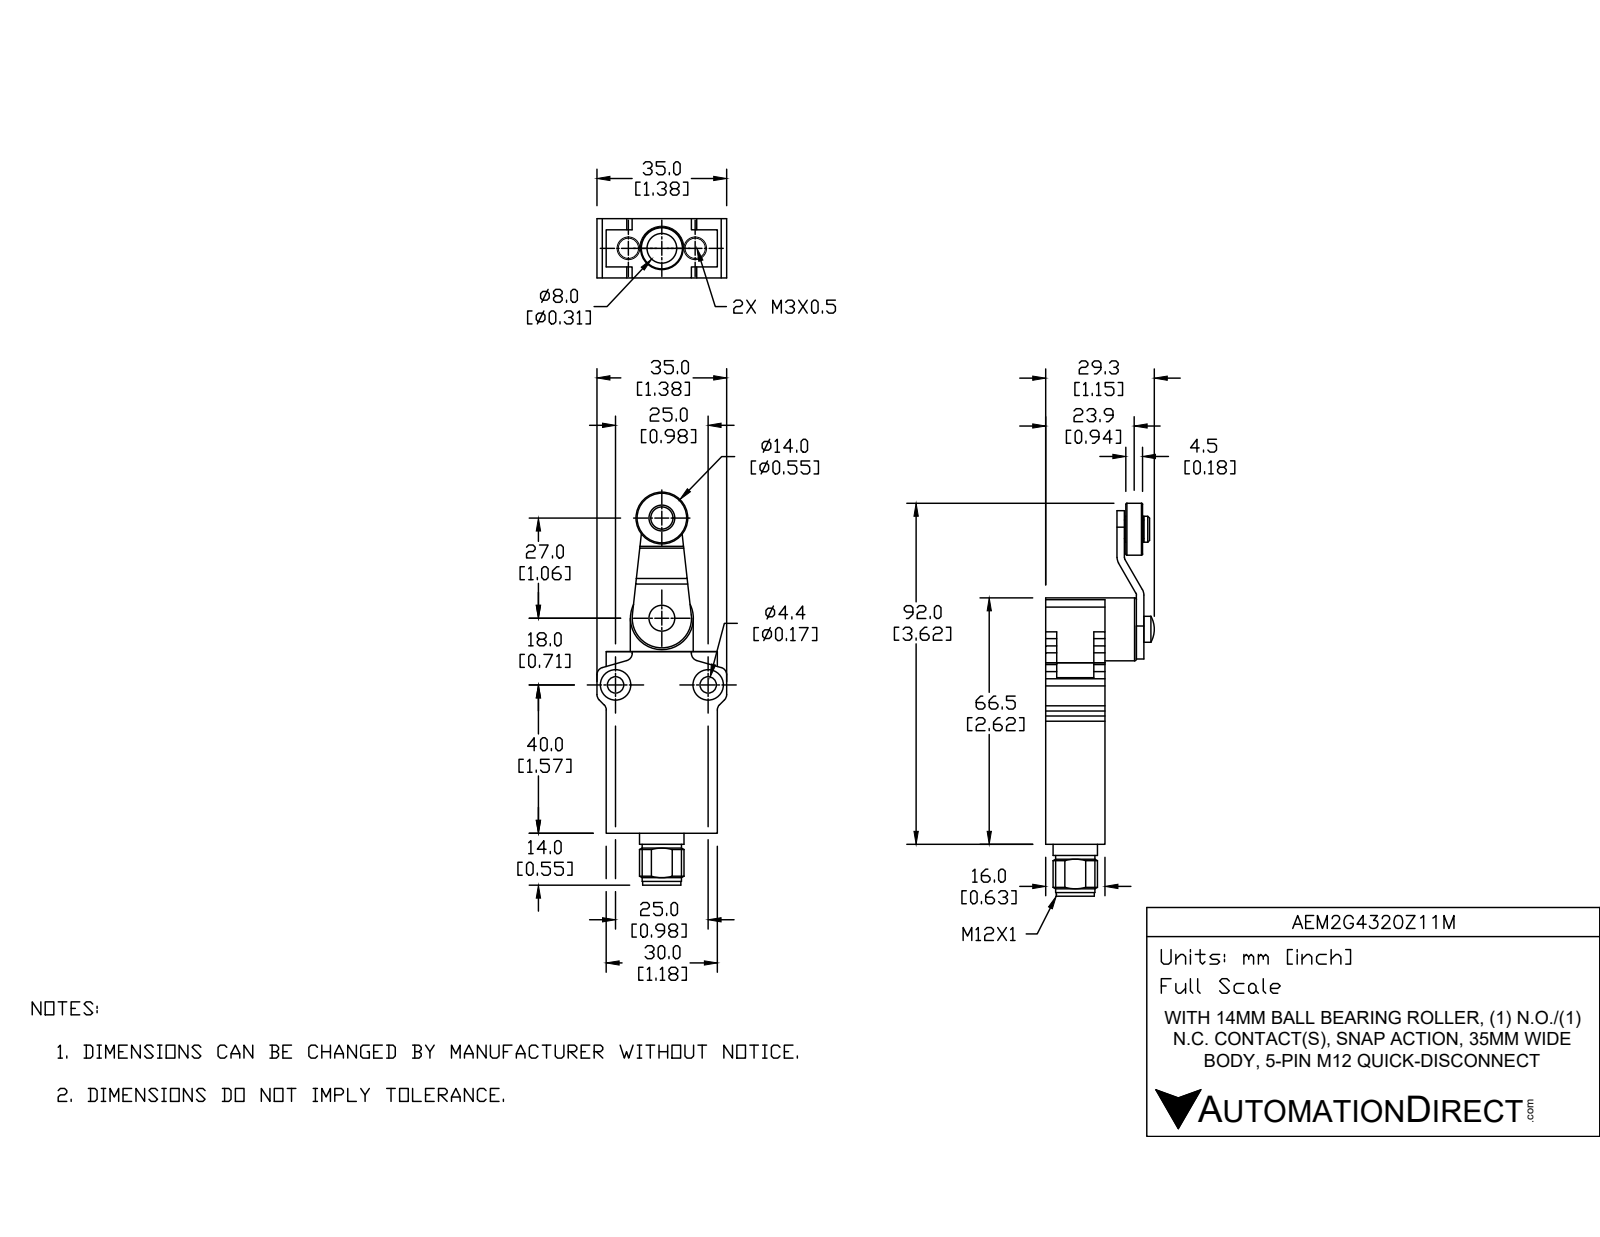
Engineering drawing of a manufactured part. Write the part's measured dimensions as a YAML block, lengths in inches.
part_name: "AEM2G4320Z11M"
step_written_by: "SolidWorks 2017 (AUTOMOTIVE_DESIGN)"
units: inches
bodies: {solids: 6, faces: 594, planar: 300, cylindrical: 93, other: 201}
overall_size: [4.272, 1.378, 1.26]
volume: 1.981
surface_area: 18.28
round_holes:
  - {diameter: 0.118, count: 2}
  - {diameter: 0.173, count: 2}
  - {diameter: 0.323, count: 2}
  - {diameter: 0.098, count: 1}
  - {diameter: 0.138, count: 1}
  - {diameter: 0.161, count: 1}
  - {diameter: 0.197, count: 1}
  - {diameter: 0.224, count: 1}
round_bosses_or_shafts:
  - {diameter: 0.276, count: 2}
  - {diameter: 0.622, count: 1}
  - {diameter: 0.551, count: 1}
  - {diameter: 0.472, count: 1}
  - {diameter: 0.417, count: 1}
  - {diameter: 0.406, count: 1}
  - {diameter: 0.394, count: 1}
  - {diameter: 0.236, count: 1}
partial_cylinders:
  - {radius: 0.079, count: 8}
  - {radius: 0.039, count: 2}
  - {radius: 0.118, count: 2}
  - {radius: 0.256, count: 1}
  - {radius: 0.315, count: 1}
face_to_face_distances: [0.63, 1.181, 0.354, 0.079, 2.047, 0.984, 0.102, 0.472, 0.433, 0.898]
hole_center_spacings: [0.748, 0.861, 0.865, 0.984, 1.043, 1.819, 1.821]
